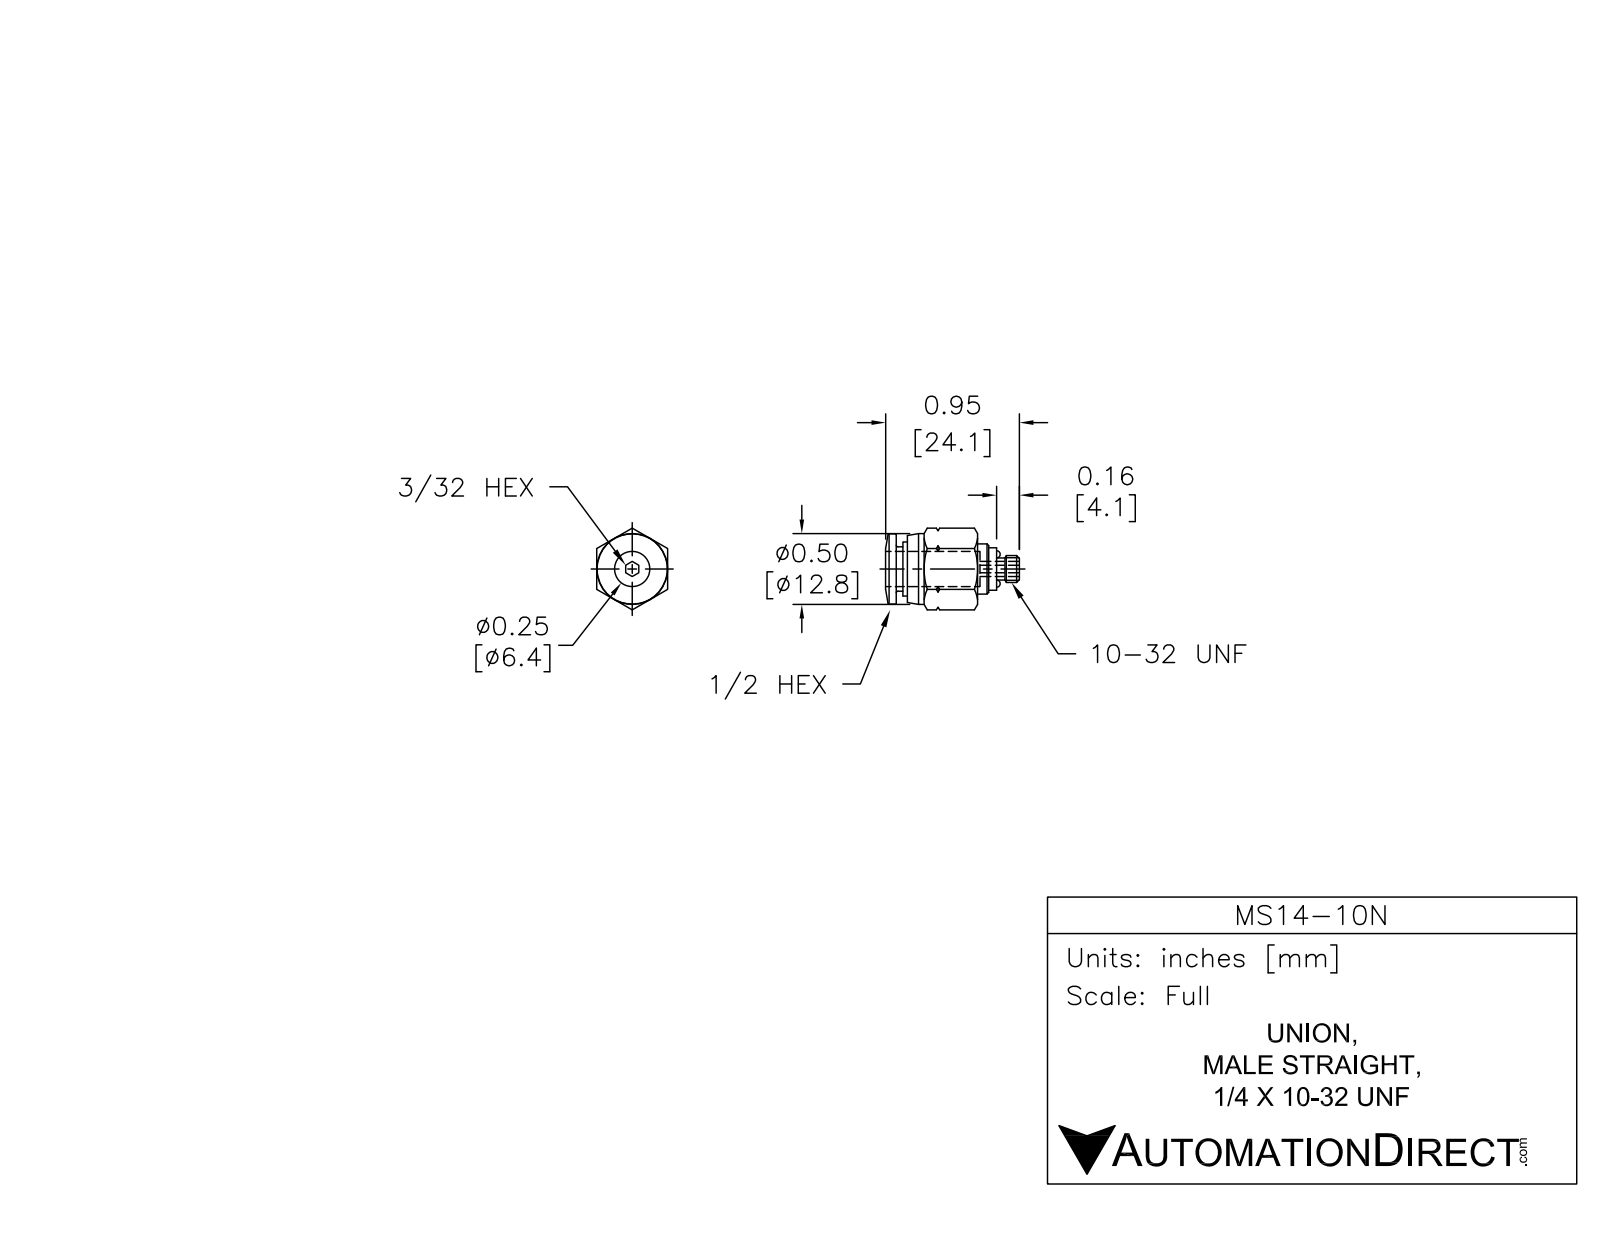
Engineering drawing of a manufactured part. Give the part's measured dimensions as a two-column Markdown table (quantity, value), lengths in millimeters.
| quantity | value |
| --- | --- |
| part name | PC1-4--U10 |
| STEP written by | Autodesk Inventor 2008 (AUTOMOTIVE_DESIGN) |
| units | millimeters |
| bodies | 2 solids, 63 faces (16 planar, 11 cylindrical, 36 other) |
| overall size | 24 × 14.66 × 12.7 |
| volume | 1 690 mm³ |
| surface area | 1 677 mm² |
| round holes (diameter × count) | 2.5 × 1, 6.55 × 1 |
| round bosses / shafts (diameter × count) | 12.7 × 1, 12.6 × 1, 9.7 × 1, 9 × 1, 7.95 × 1, 7.6 × 1, 4.83 × 1, 3.95 × 1 |
| main face-to-face distances | 12.7, 14.6, 2, 12.6, 0.8, 0.4, 13, 15, 13.8, 13.4 |
